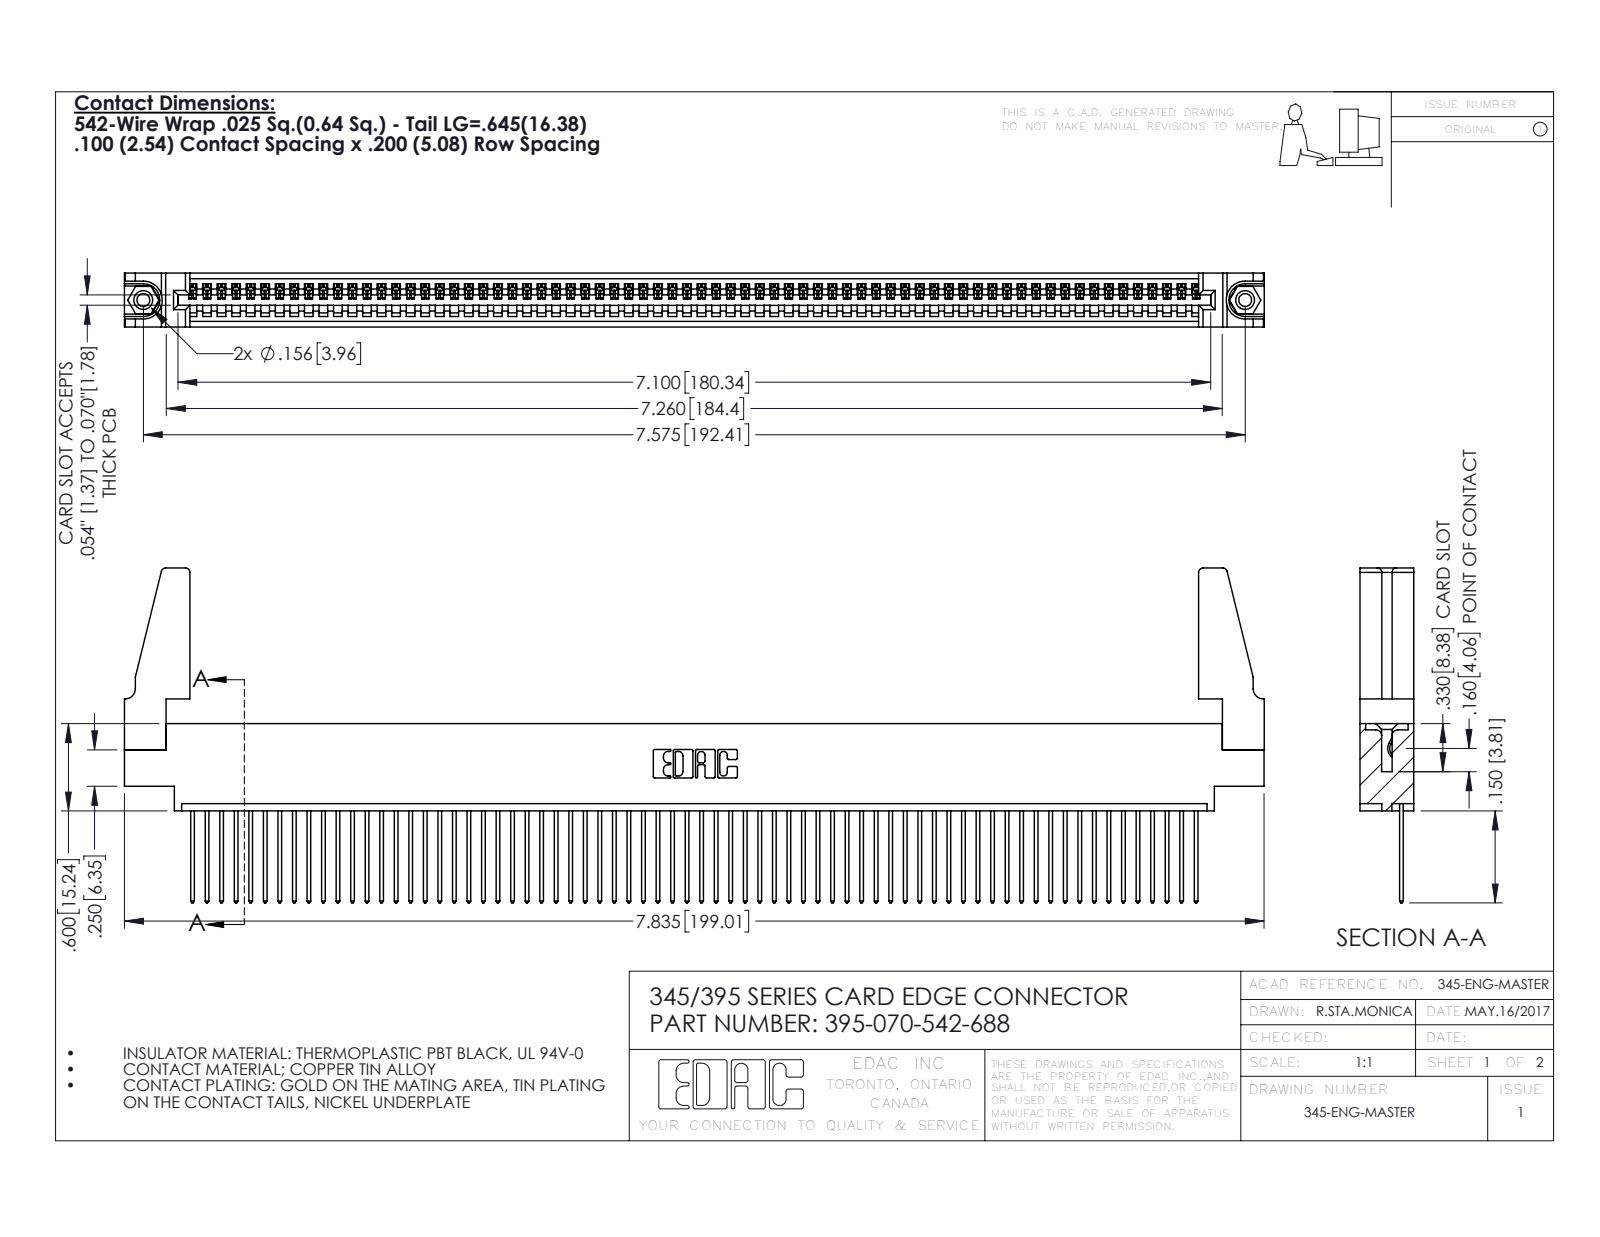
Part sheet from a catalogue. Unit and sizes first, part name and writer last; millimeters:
Units: millimetres
Overall size (bounding box): 199 × 58.5 × 9.4
Round holes (diameter × count): ⌀2.3 ×2, ⌀3.2 ×2, ⌀4 ×2, ⌀1.6 ×1
Round bosses / shafts (diameter × count): ⌀3.9 ×2
Partial cylindrical surfaces — rounded edges, fillets, slot ends (radius × count): R0.2 ×140, R0.3 ×140, R0.3 ×22, R0.8 ×8, R0.2 ×6, R0.8 ×6, R0.7 ×3, R0.8 ×2
Main face-to-face distances: 1.8, 7.6, 9.4, 2.5, 6.9, 0.6, 5.1, 5.7, 4.4, 3.8
Hole centre spacings: 6.9, 186.4, 192.4
Volume: 22 430 mm³ · Surface area: 30 100 mm²
Bodies: 75 solids, 4314 faces (2956 planar, 1342 cylindrical, 16 other)
Part name (STEP PRODUCT): 345-220-078_345-220-088; 395-070-542-688; 345 Part_0.170 Offset - 0.156 Dia-TH; 345-250-001_345-250-001-102 (+1 more)
STEP written by: SolidWorks 2016 (CONFIG_CONTROL_DESIGN)
